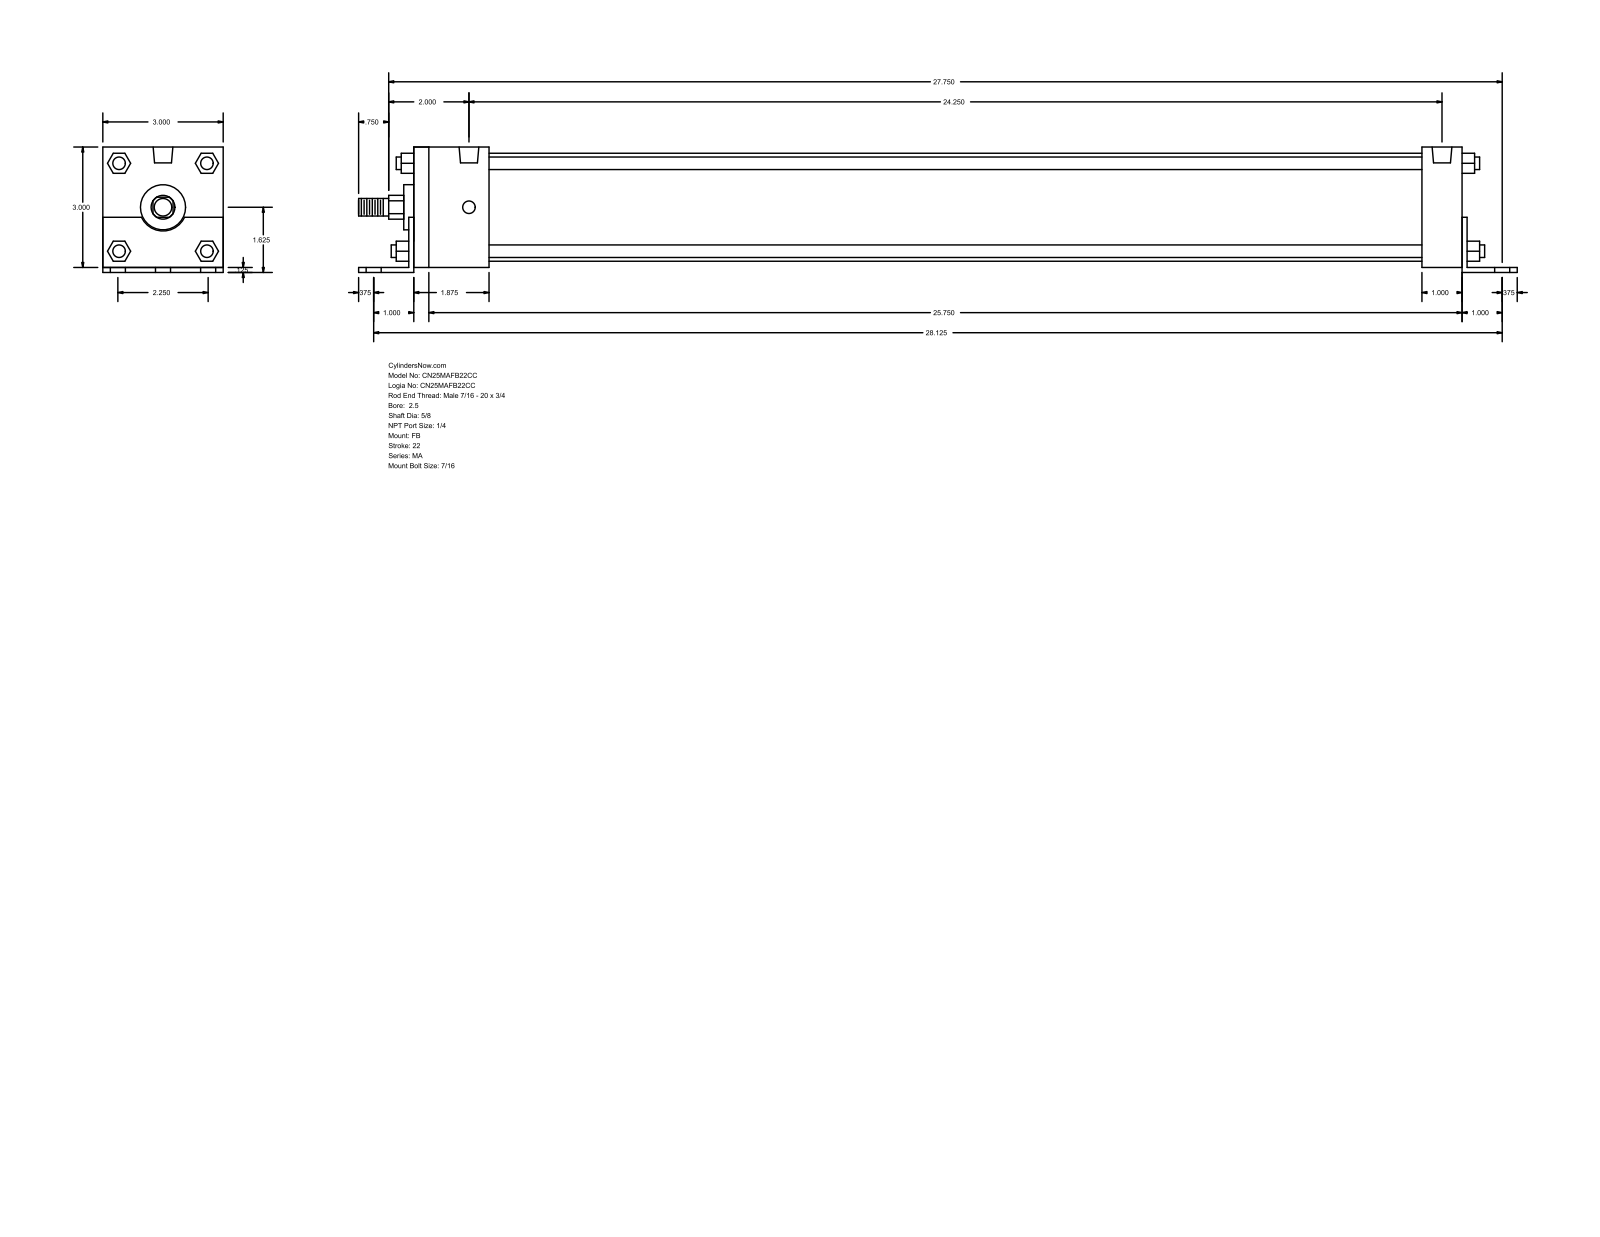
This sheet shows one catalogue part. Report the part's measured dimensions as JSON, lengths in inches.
{"part_name": "MA_FB__0250_0.625", "step_written_by": "GSSL Pune (CONFIG_CONTROL_DESIGN)", "units": "inches", "bodies": {"solids": 0, "faces": 140, "planar": 105, "cylindrical": 35, "other": 0}, "overall_size": [28.875, 3.125, 3], "round_holes": [[0.437, 6], [0.313, 4], [0.492, 2]], "round_bosses_or_shafts": [[0.313, 4], [2.69, 1], [1.125, 1], [0.625, 1], [0.437, 1]], "partial_cylinders_radius": [[0.297, 1], [0.593, 1]], "face_to_face_distances": [3, 0.125, 3.125, 26.125, 26.375, 0.125, 26.25, 1.875, 1, 26.25], "hole_center_spacings": [1.125, 28.148, 28.125, 1.875, 2.25, 2.628, 24.25, 25.774]}
